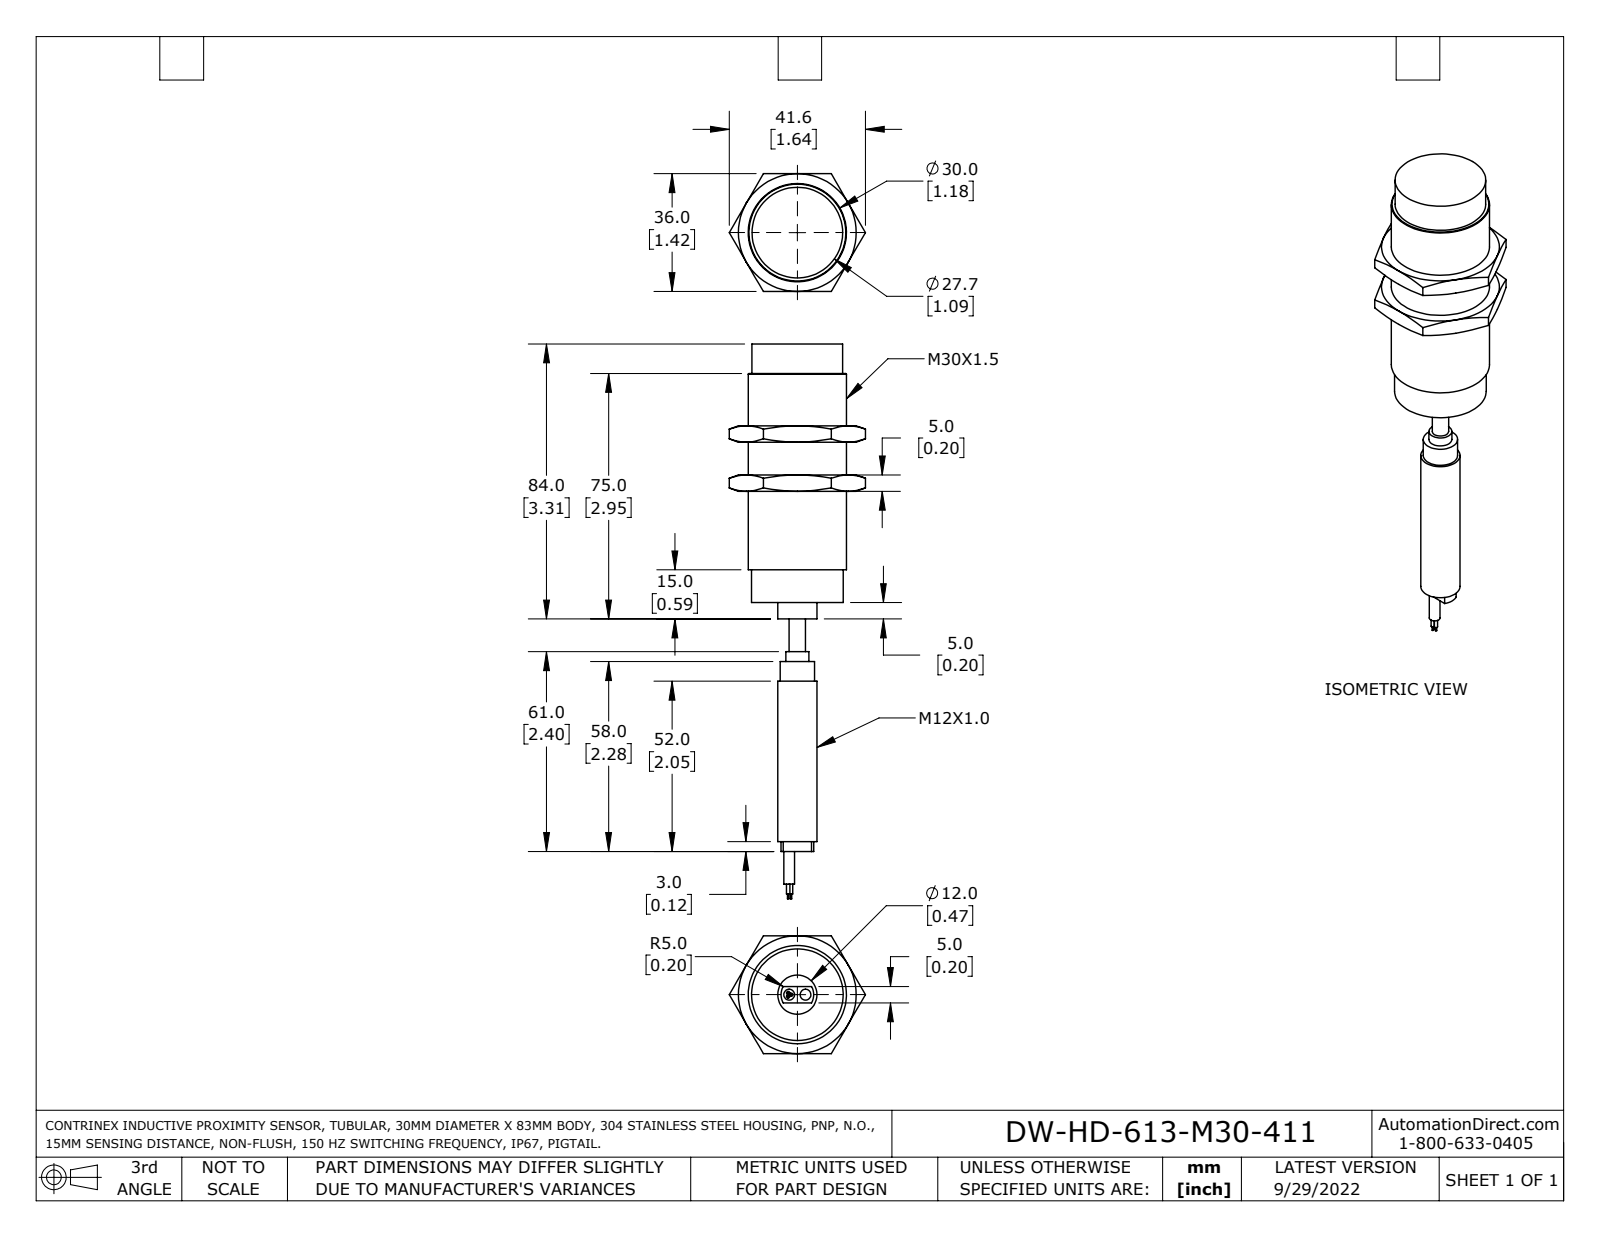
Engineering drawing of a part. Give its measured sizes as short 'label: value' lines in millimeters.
name: DW-HD-613-M30-411
written by: SolidWorks 2021 (AUTOMOTIVE_DESIGN)
unit: mm
bodies: 1 solid, 81 faces (36 planar, 20 cylindrical, 25 other)
size: 169.5 × 41.6 × 36
volume: 65 170 mm³; area: 13 440 mm²
holes: 1× ⌀3.3
bosses: 3× ⌀1, 3× ⌀0.4, 1× ⌀30, 1× ⌀28, 1× ⌀27.7, 1× ⌀12, 1× ⌀10.5, 1× ⌀7
rounds: 1× R5
face distances: 5, 15, 36, 79, 39, 10, 54, 49, 34, 25
